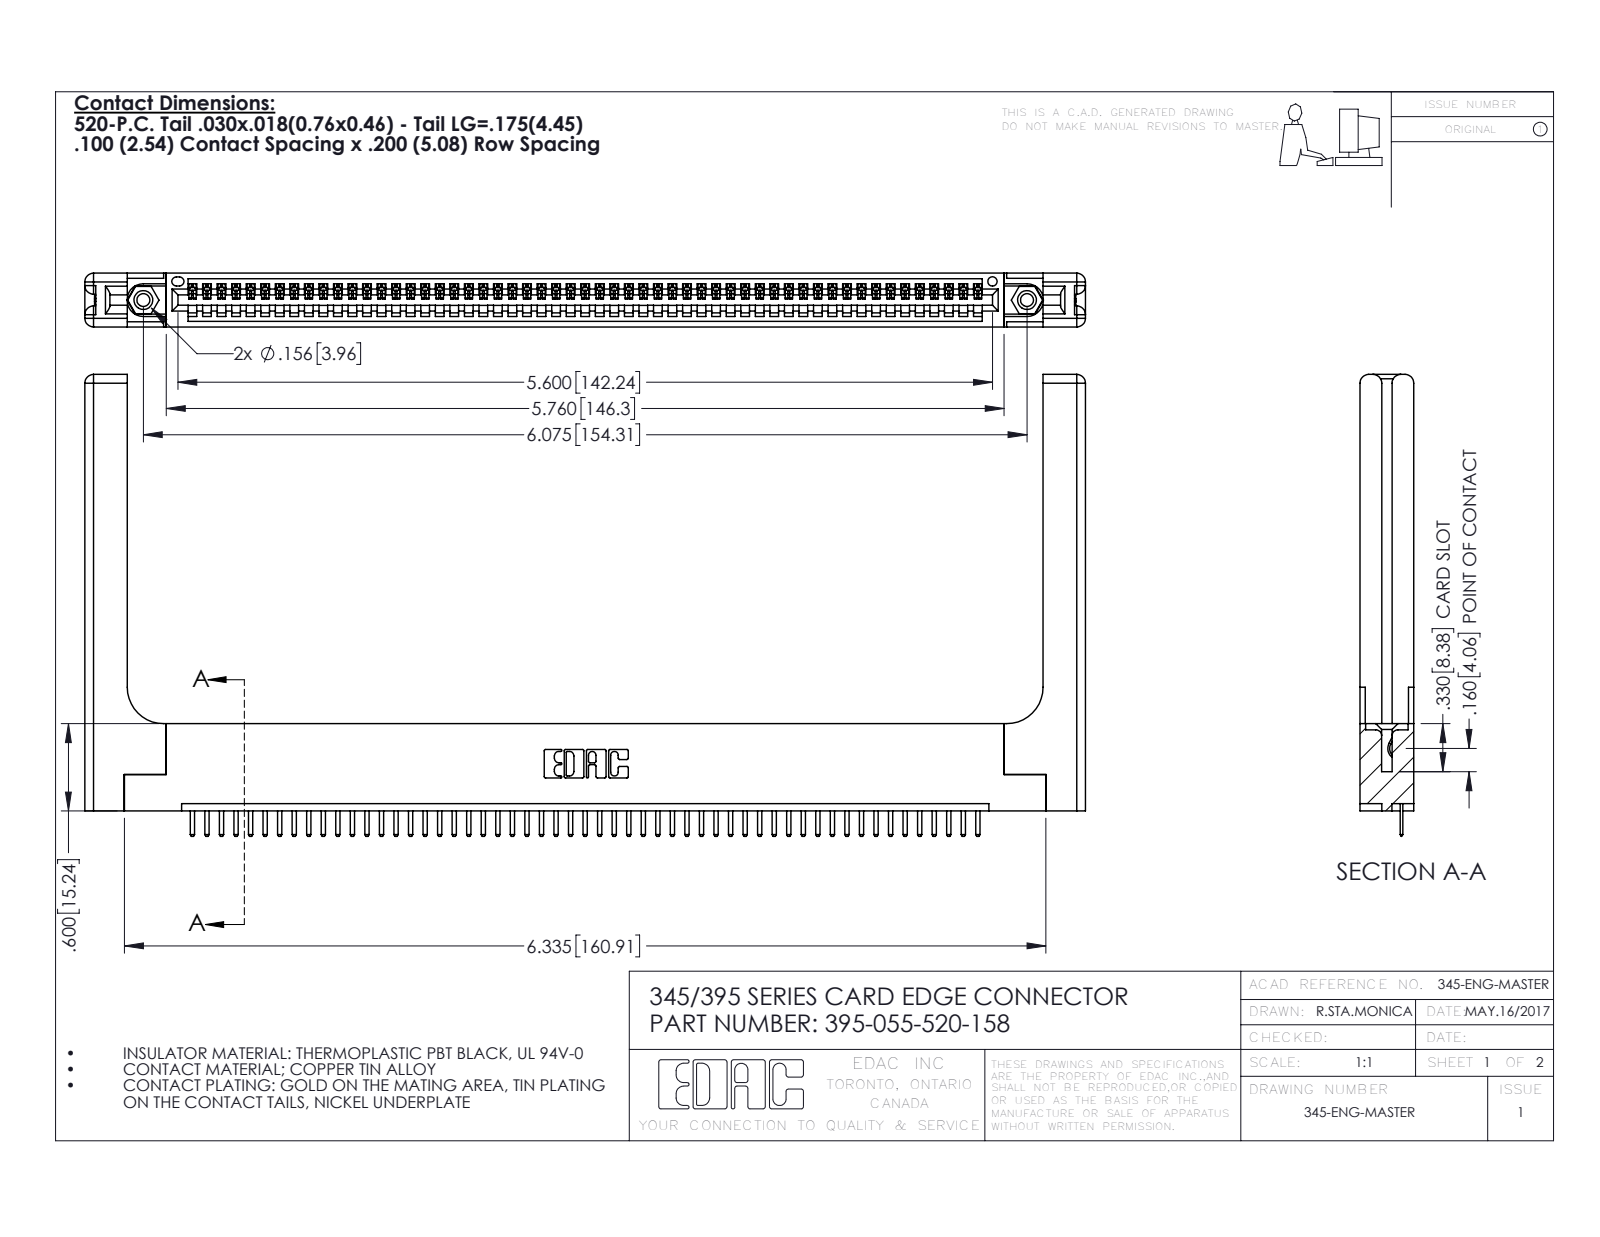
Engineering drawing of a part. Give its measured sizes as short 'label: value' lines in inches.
name: 395-055-520-158; 345-220-058_345-220-058; 345-250-001_345-250-001-102; 345-292-001_345-293-120 (+1 more)
written by: SolidWorks 2016 (CONFIG_CONTROL_DESIGN)
unit: in
bodies: 60 solids, 3792 faces (2538 planar, 1194 cylindrical, 60 other)
size: 6.879 × 3.175 × 0.37
volume: 1.529 in³; area: 41.77 in²
holes: 2× ⌀0.089, 2× ⌀0.125, 2× ⌀0.156, 1× ⌀0.064
bosses: 2× ⌀0.155
rounds: 112× R0.01, 110× R0.006, 22× R0.01, 16× R0.06, 6× R0.007, 6× R0.031, 3× R0.026, 2× R0.03
face distances: 0.37, 0.072, 0.298, 0.2, 0.098, 0.272, 0.025, 0.225, 0.148, 0.15
hole spacings: 0.27, 5.839, 6.075
